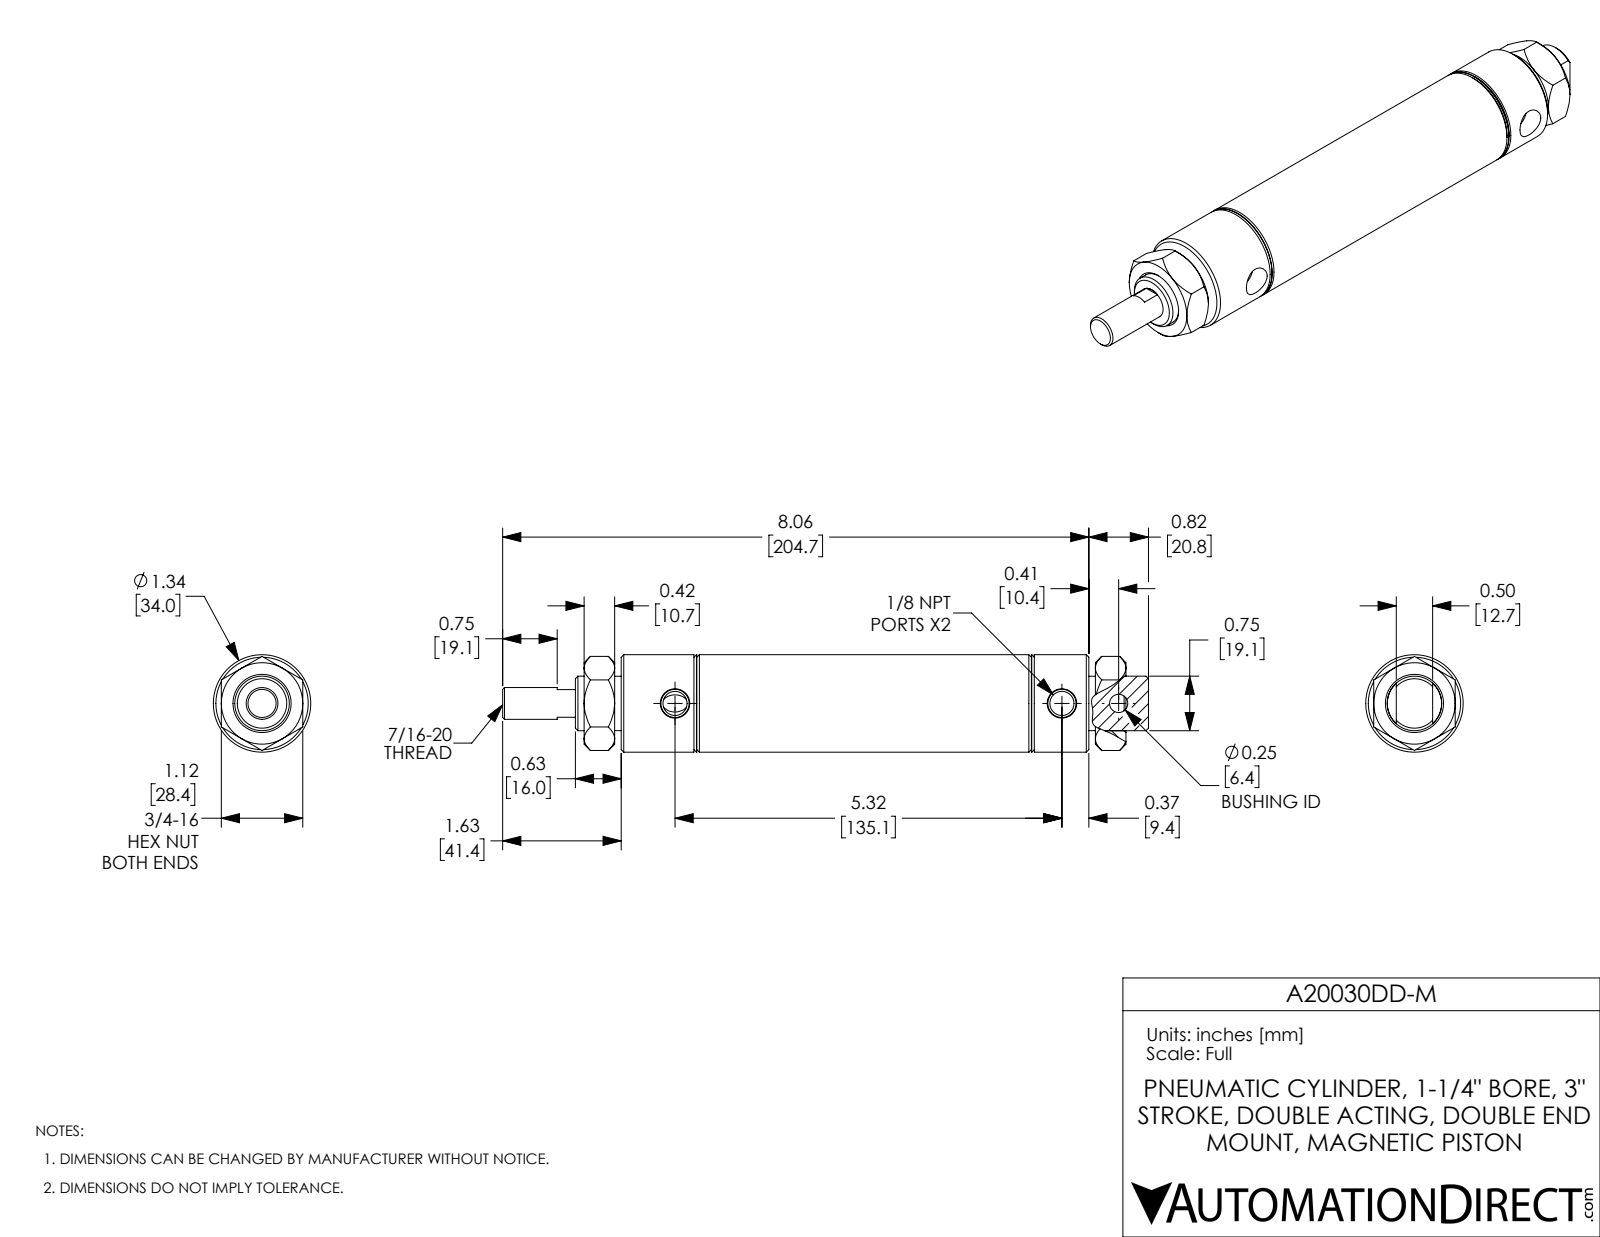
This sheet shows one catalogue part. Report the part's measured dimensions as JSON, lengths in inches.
{"part_name": "A20030DD-M-MainBody; A20030DD-M-Rod; A20030DD-M_Mounting Nut_D-3556; A20030DD-M", "step_written_by": "SolidWorks 2017 (AUTOMOTIVE_DESIGN)", "units": "inches", "bodies": {"solids": 4, "faces": 138, "planar": 44, "cylindrical": 36, "other": 58}, "overall_size": [8.88, 1.34, 1.34], "volume_in3": 6.938, "surface_area_in2": 73.88, "round_holes": [[0.332, 2], [0.251, 1], [0.437, 1], [0.75, 1], [1.25, 1]], "round_bosses_or_shafts": [[1.34, 1], [0.747, 1]], "face_to_face_distances": [1.465, 4.965, 0.5, 1.12, 3.5, 3, 0.31, 0.42, 7.03, 1.965], "hole_center_spacings": [0.78, 5.32, 6.1]}
